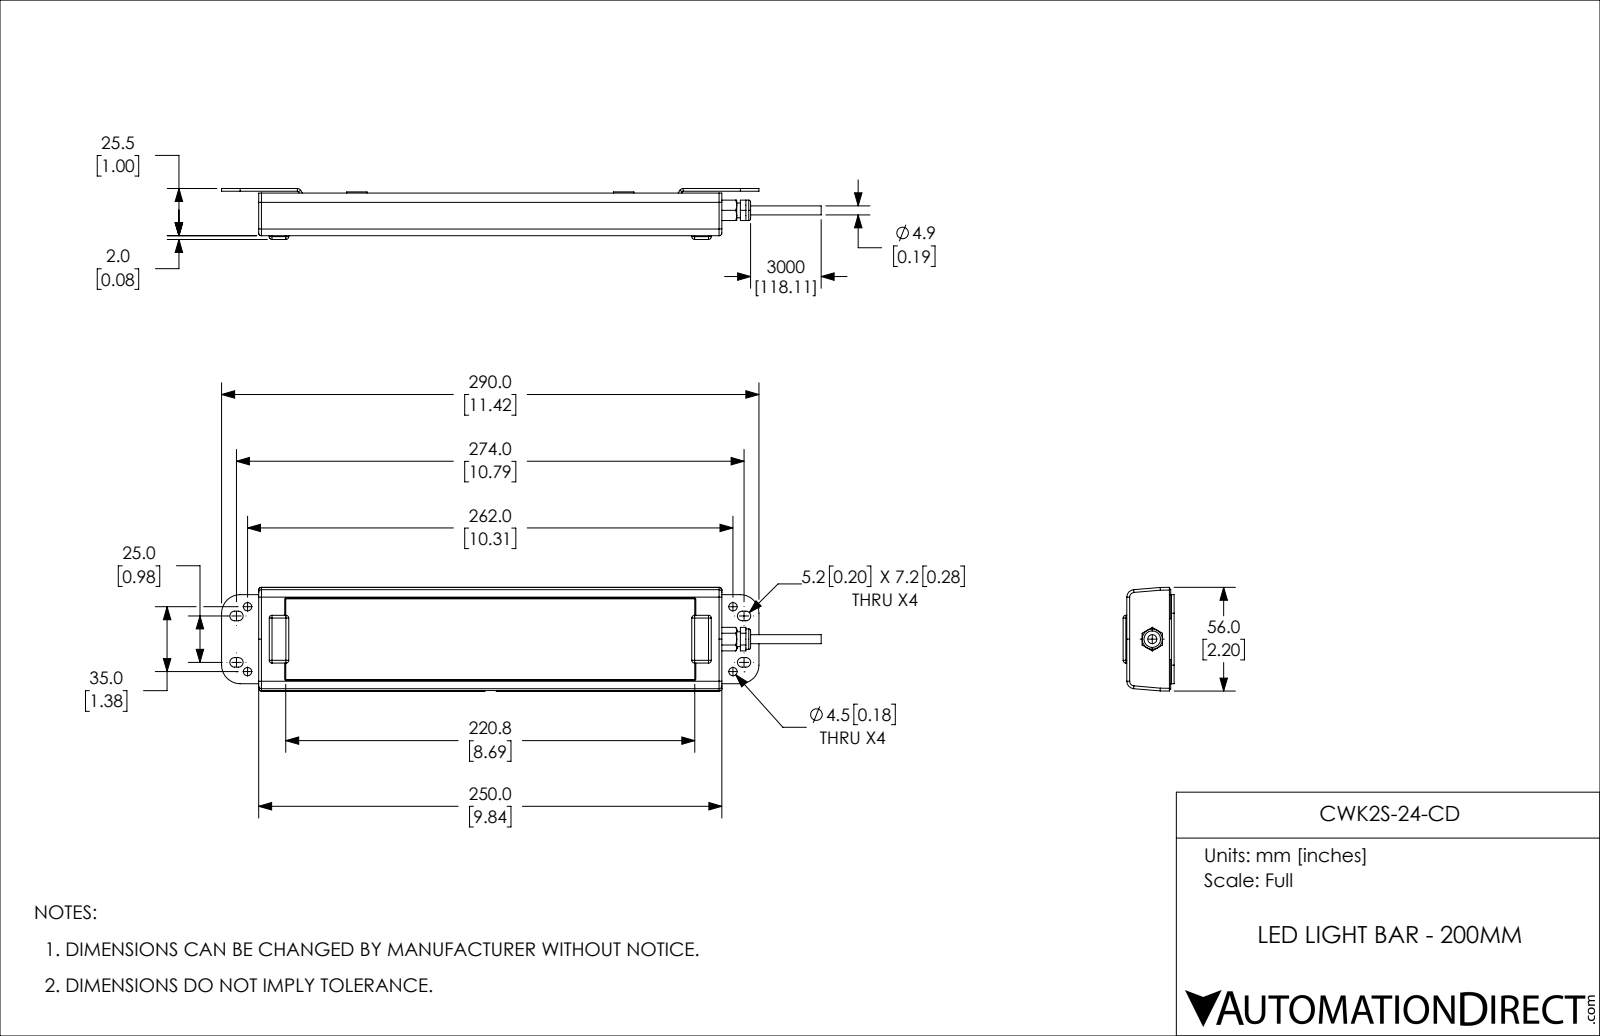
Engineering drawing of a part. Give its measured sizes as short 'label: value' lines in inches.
name: CWK2S-24-CD
written by: SolidWorks 2018 (AUTOMOTIVE_DESIGN)
unit: in
bodies: 7 solids, 411 faces (208 planar, 126 cylindrical, 77 other)
size: 12.74 × 2.205 × 1.083
volume: 14.27 in³; area: 107.1 in²
holes: 4× ⌀0.157, 4× ⌀0.177, 2× ⌀0.165
bosses: 5× ⌀0.433, 2× ⌀0.37, 2× ⌀0.256, 1× ⌀0.315, 1× ⌀0.193
rounds: 22× R0.059, 12× R0.079, 8× R0.083, 8× R0.102, 4× R0.024, 4× R0.394, 2× R0.02, 2× R0.157
face distances: 0.697, 0.059, 0.248, 0.307, 1.004, 0.945, 0.269, 1.739, 0.711, 0.652
hole spacings: 1.616, 2.174, 8.701, 8.822, 1.378, 1.535, 7.087, 7.251
